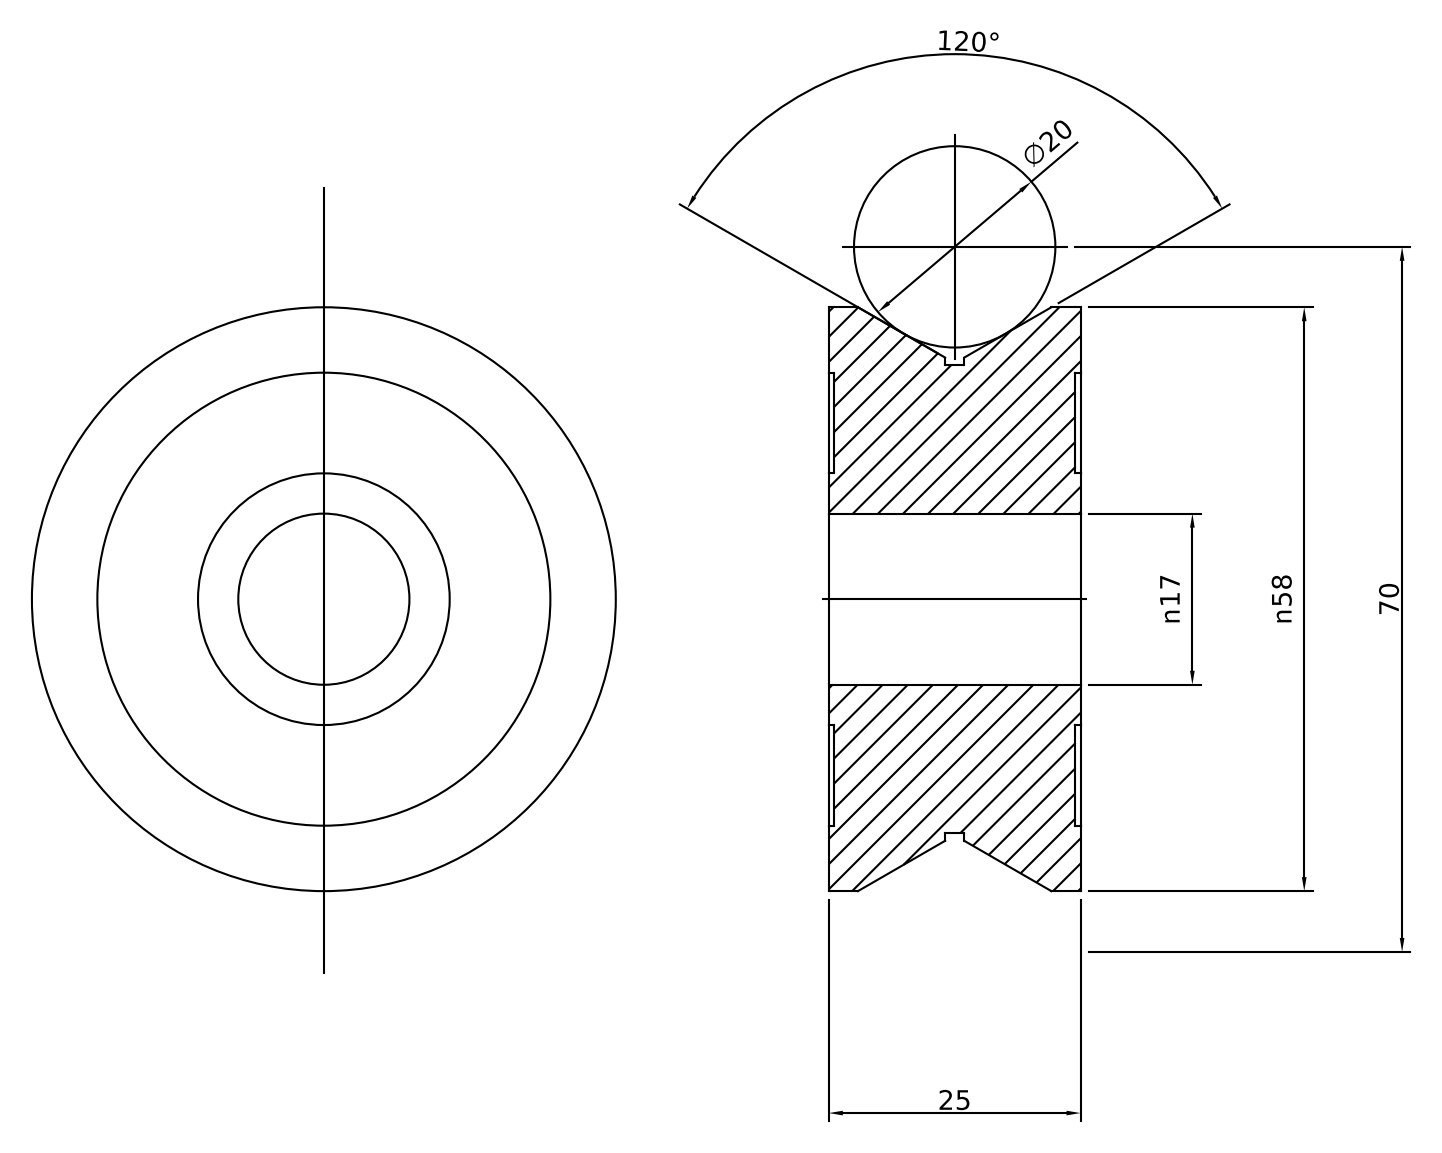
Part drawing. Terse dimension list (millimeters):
name: 80RT00016R-A
written by: Autodesk Inventor 2022 (AUTOMOTIVE_DESIGN)
unit: mm
bodies: 1 solid, 18 faces (8 planar, 8 cylindrical, 2 other)
size: 58 × 58 × 25
volume: 50 052 mm³; area: 11 269 mm²
holes: 1× ⌀17, 1× ⌀45
bosses: 1× ⌀58, 1× ⌀46.5, 1× ⌀25
face distances: 0.5, 24.5, 25, 24, 11.55, 13.45, 11.05, 12.95, 1.9
